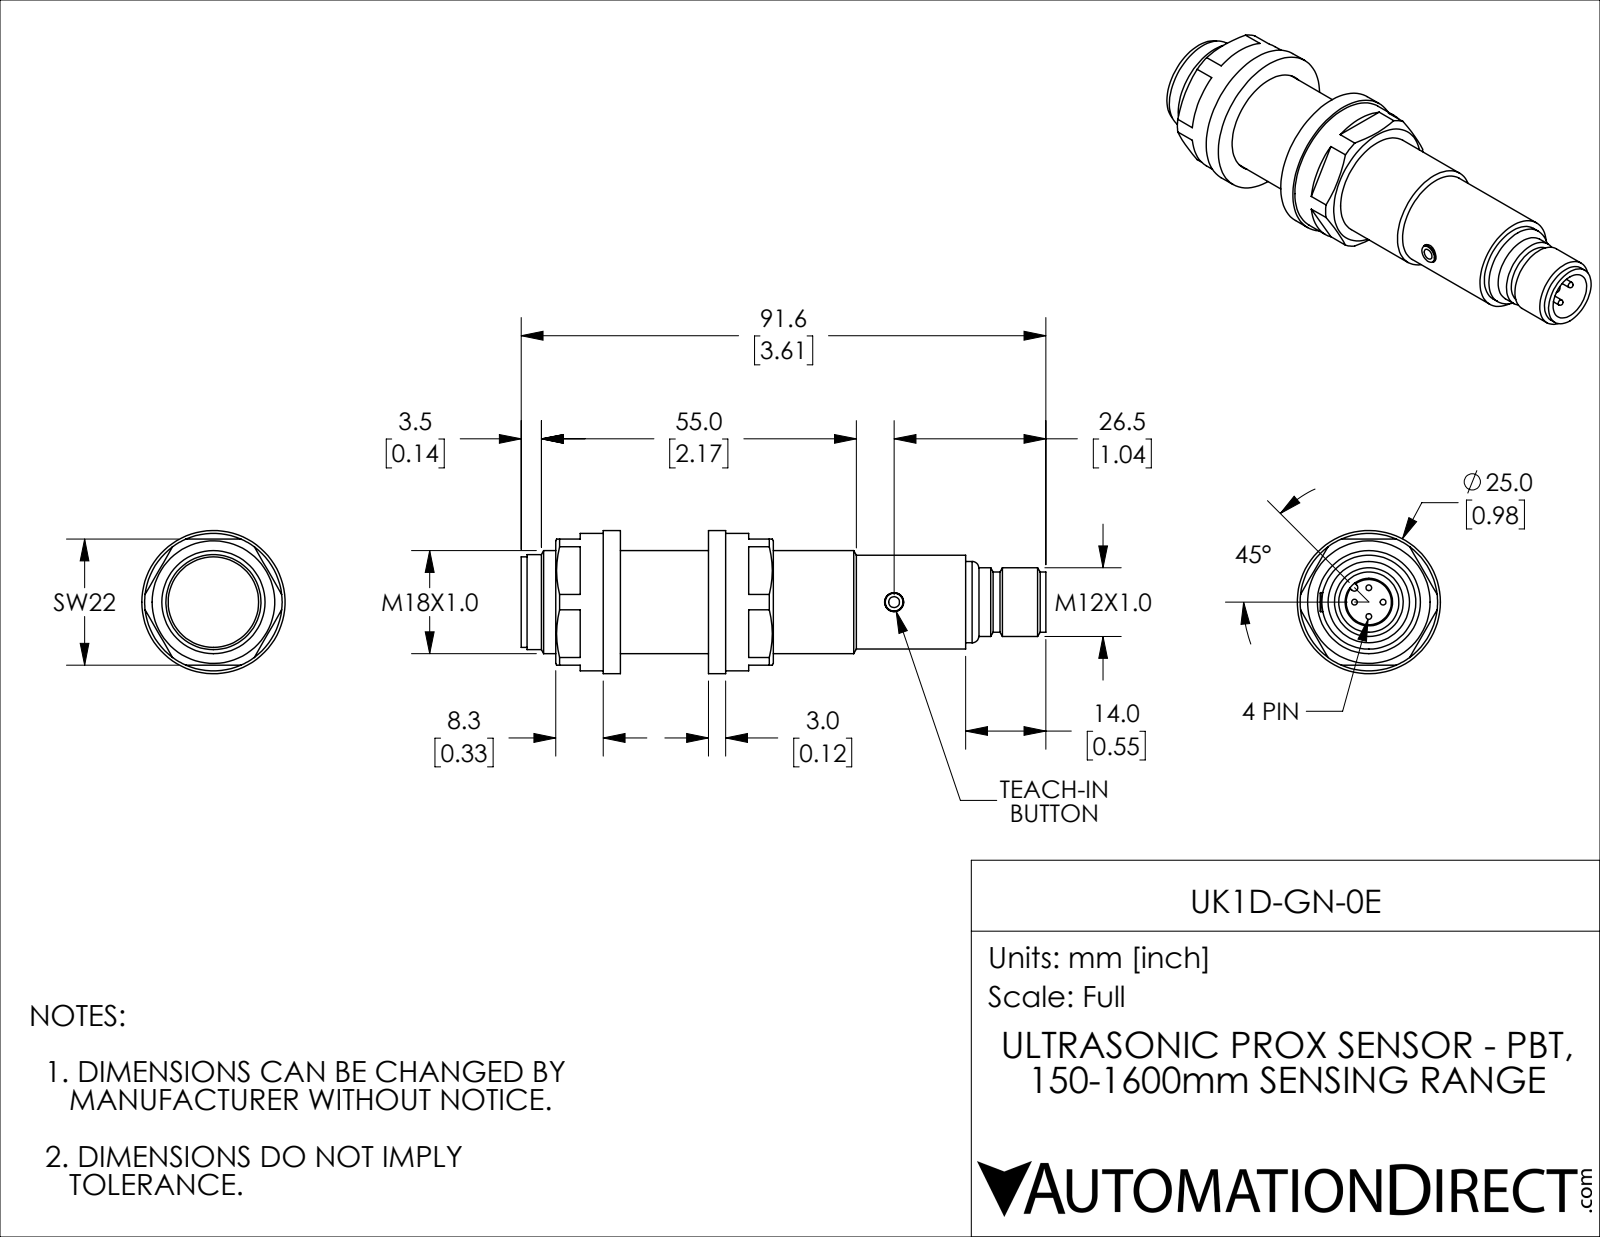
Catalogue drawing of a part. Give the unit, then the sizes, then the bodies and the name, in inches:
Units: inches
Overall size (bounding box): 3.606 × 0.984 × 0.984
Round holes (diameter × count): ⌀0.13 ×1, ⌀0.327 ×1, ⌀0.709 ×1, ⌀0.717 ×1
Round bosses / shafts (diameter × count): ⌀0.039 ×4, ⌀0.984 ×1, ⌀0.945 ×1, ⌀0.654 ×1, ⌀0.646 ×1, ⌀0.622 ×1, ⌀0.559 ×1, ⌀0.472 ×1
Partial cylindrical surfaces — rounded edges, fillets, slot ends (radius × count): R0.024 ×1
Main face-to-face distances: 0.118, 0.724, 0.843, 0.606, 0.866, 0.327, 0.445, 1.051, 1.169, 0.563
Volume: 1.477 in³ · Surface area: 16.01 in²
Bodies: 6 solids, 123 faces (43 planar, 49 cylindrical, 31 other)
Part name (STEP PRODUCT): UK1D-GN-0E
STEP written by: SolidWorks 2018 (AUTOMOTIVE_DESIGN)
